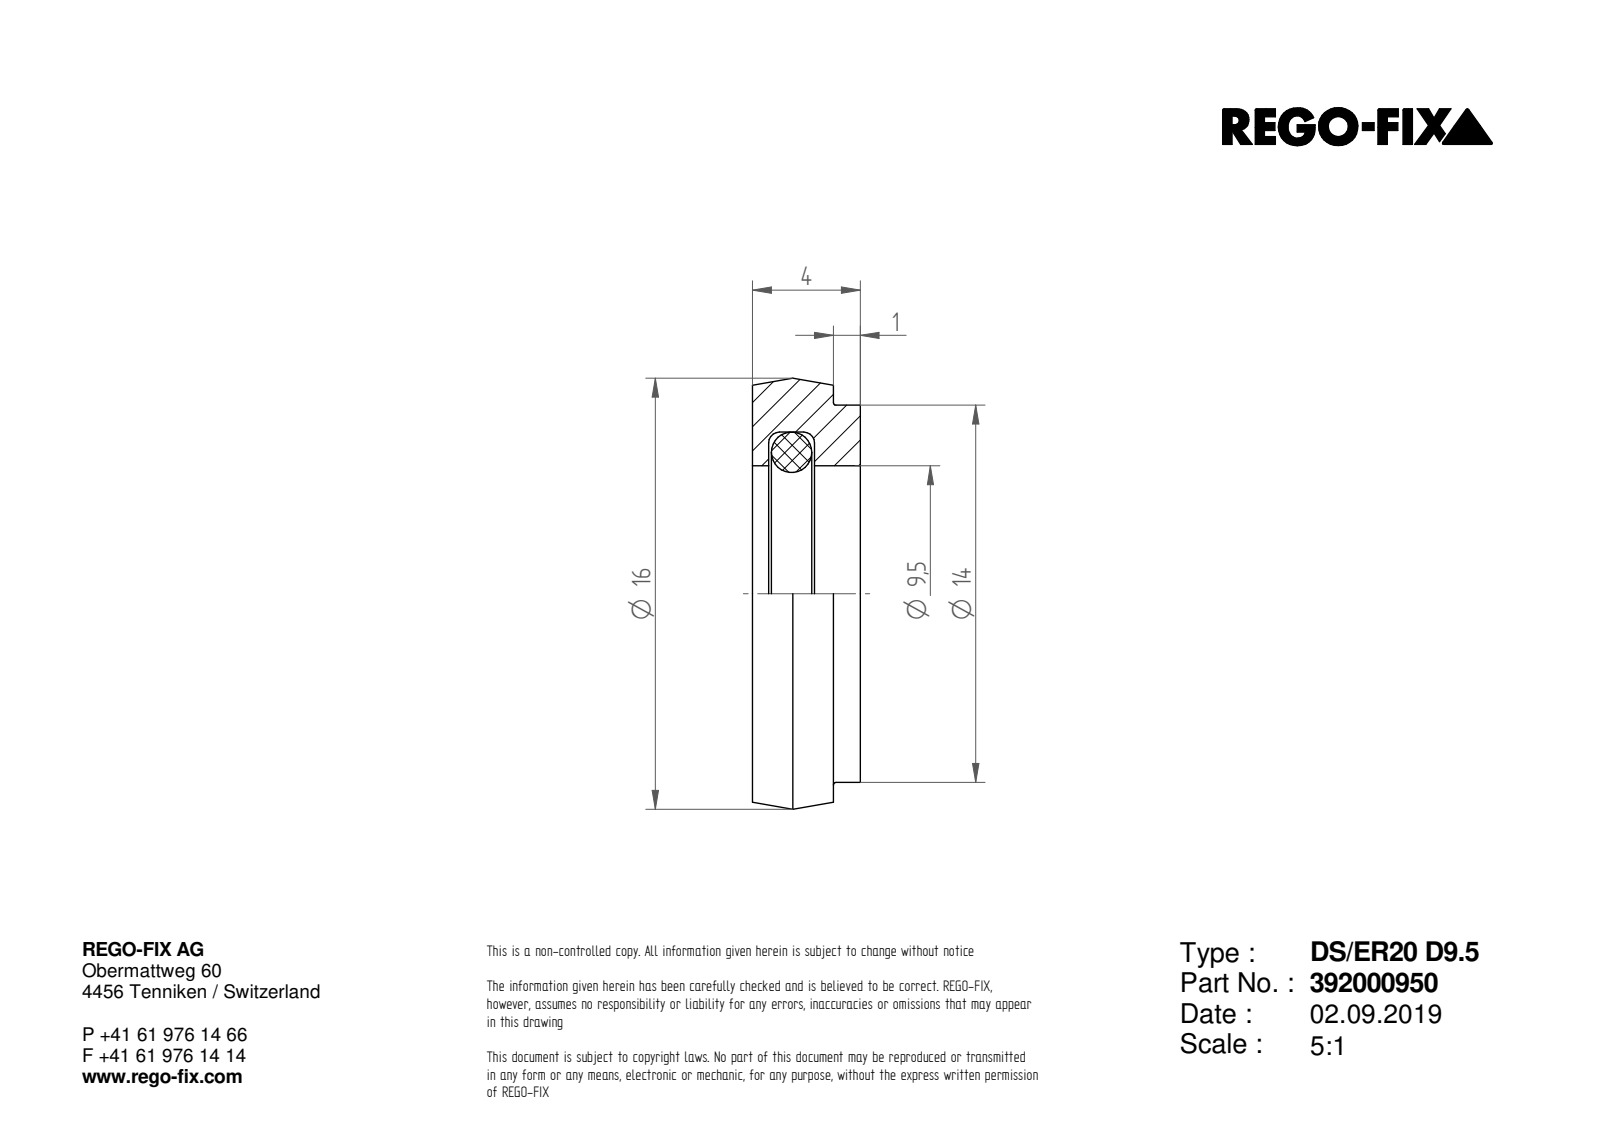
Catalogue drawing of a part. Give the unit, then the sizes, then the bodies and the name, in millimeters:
Units: millimetres
Overall size (bounding box): 16 × 16 × 4
Round holes (diameter × count): ⌀9.5 ×1
Round bosses / shafts (diameter × count): ⌀16 ×1, ⌀14 ×1
Main face-to-face distances: 4, 1, 3
Volume: 474 mm³ · Surface area: 573 mm²
Bodies: 1 solid, 7 faces (3 planar, 3 cylindrical, 1 other)
Part name (STEP PRODUCT): NOCUT
STEP written by: SIEMENS PLM Software Solid Edge ST10 (AUTOMOTIVE_DESIGN)
